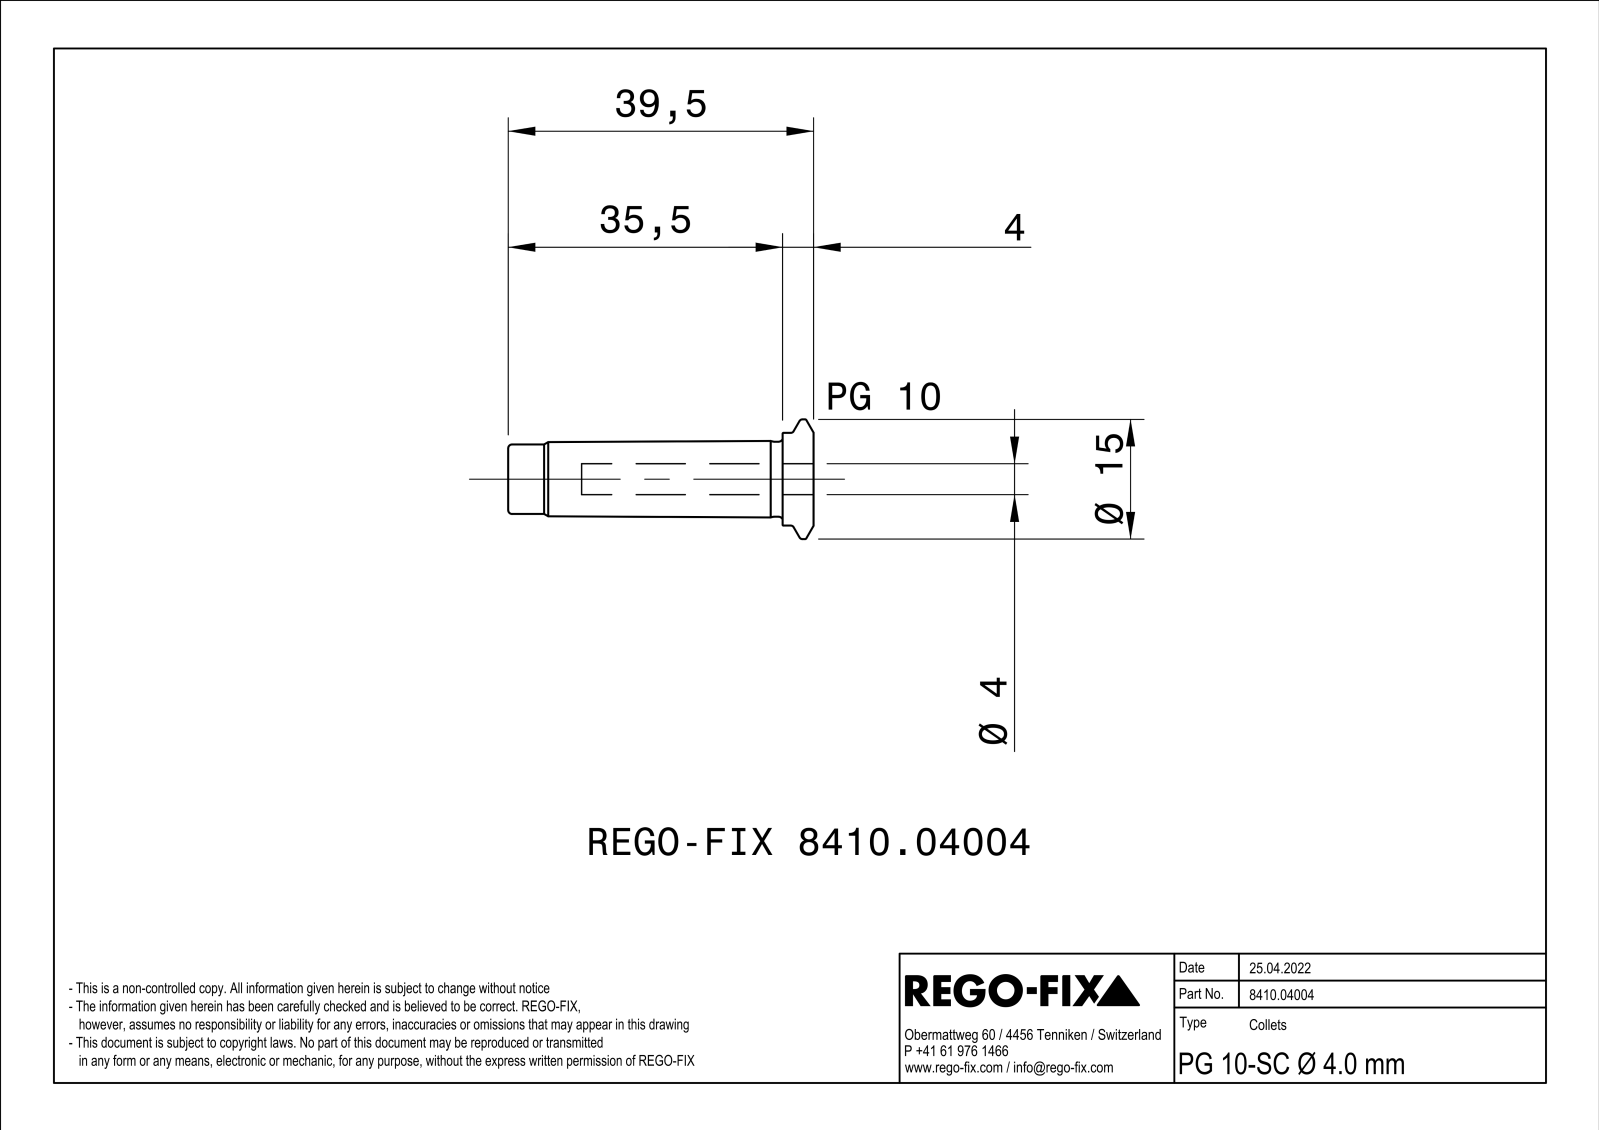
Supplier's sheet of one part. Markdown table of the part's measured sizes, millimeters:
| quantity | value |
| --- | --- |
| part name | NOCUT |
| STEP written by | SIEMENS PLM Software Solid Edge ST10 (AUTOMOTIVE_DESIGN) |
| units | millimeters |
| bodies | 1 solid, 49 faces (11 planar, 18 cylindrical, 20 other) |
| overall size | 39.5 × 15.5 × 15.5 |
| volume | 2 400 mm³ |
| surface area | 2 530 mm² |
| round holes (diameter × count) | 1.5 × 2, 4 × 1, 6.19 × 1 |
| round bosses / shafts (diameter × count) | 15.5 × 1, 12 × 1, 9.7 × 1, 9 × 1 |
| partial cylindrical surfaces (radius × count) | 0.15 × 4 |
| main face-to-face distances | 39.5, 4, 35.5 |
